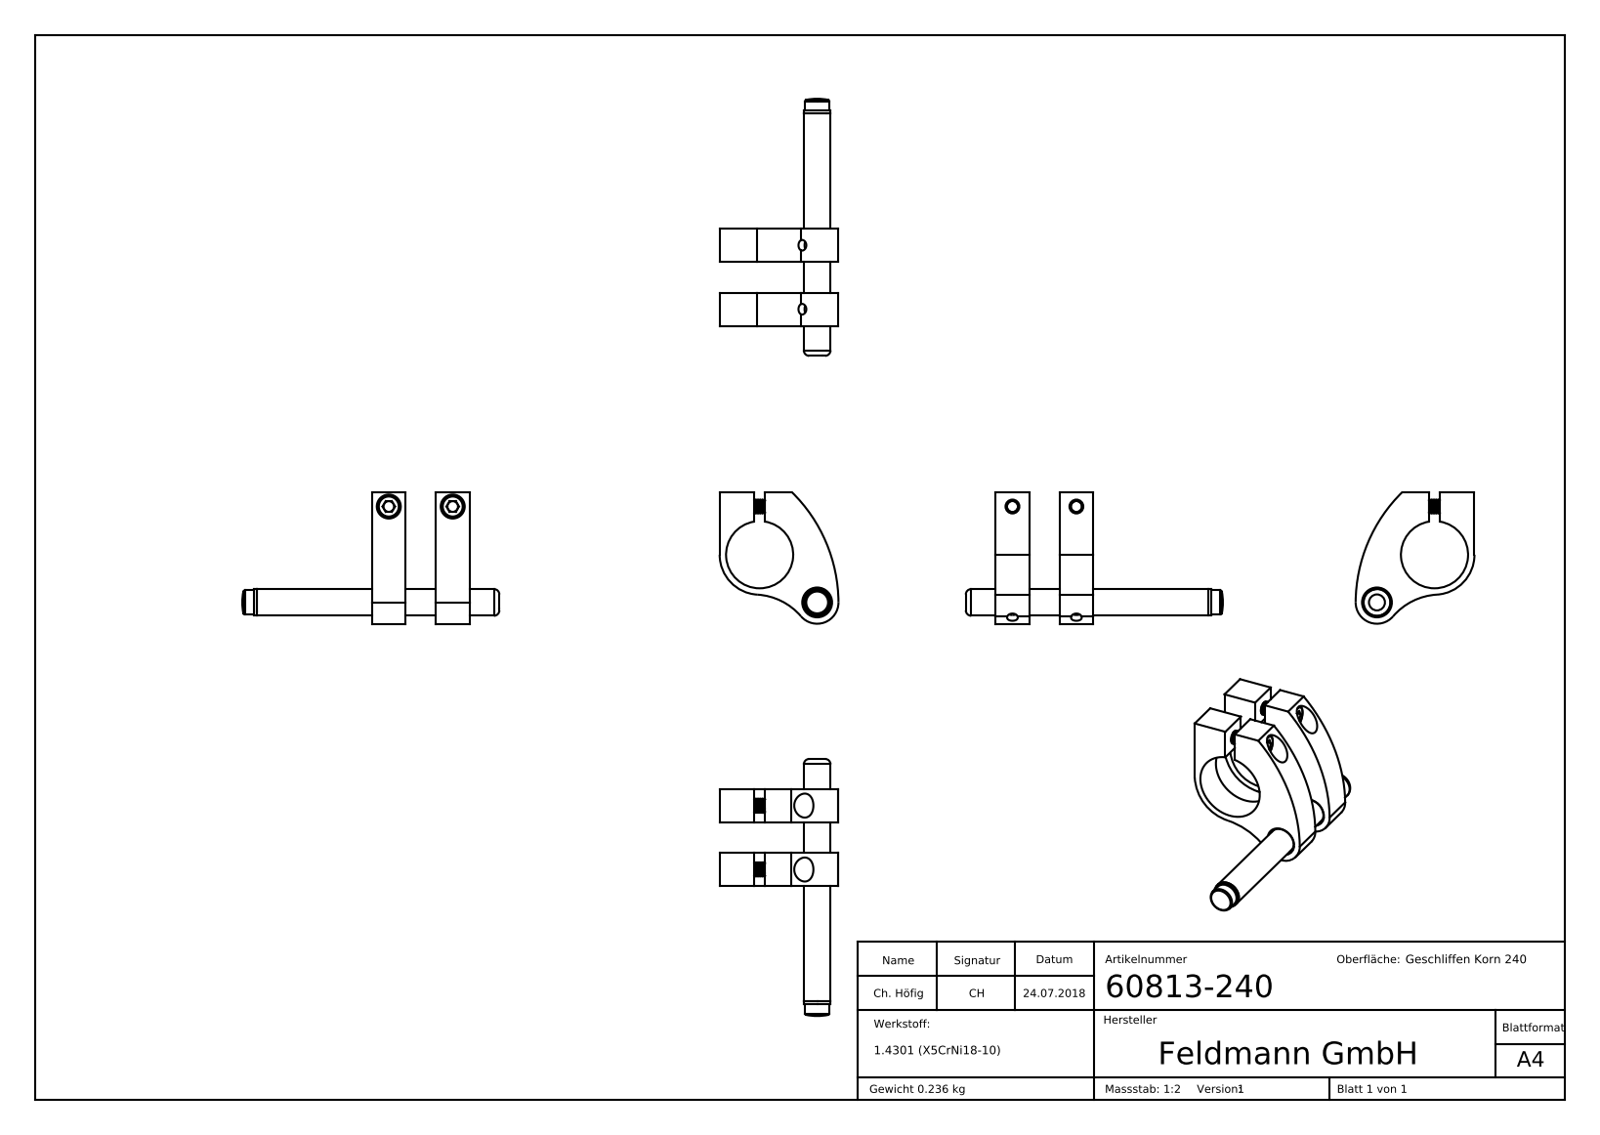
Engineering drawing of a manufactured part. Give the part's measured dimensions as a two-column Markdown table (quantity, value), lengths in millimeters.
| quantity | value |
| --- | --- |
| part name | 60813-240 Teil3_60813-240 Teil3; socket head cap screw_din_DIN 912 M5 x 20 --- 20S; socket set screw cone point_din_DIN 914 - M4 x 6-S; 60813-240 Teil2_60813-240 Teil2 (+2 more) |
| STEP written by | SolidWorks 2015 (CONFIG_CONTROL_DESIGN) |
| units | millimeters |
| bodies | 8 solids, 764 faces (160 planar, 212 cylindrical, 392 other) |
| overall size | 96.5 × 49.5 × 44.6 |
| volume | 31 434 mm³ |
| surface area | 17 352 mm² |
| round holes (diameter × count) | 3.3 × 2, 4 × 2, 4.2 × 2, 5.2 × 2, 5.5 × 2, 9 × 2, 5 × 1, 10.2 × 1, 25.2 × 1 |
| round bosses / shafts (diameter × count) | 8.5 × 2, 5 × 2, 4 × 2, 10 × 1, 9 × 1 |
| partial cylindrical surfaces (radius × count) | 2.6 × 1, 8 × 1, 15 × 1, 23.5 × 1, 58.5 × 1 |
| main face-to-face distances | 24, 12.5, 36.5, 11.5, 13, 17, 4, 22.8, 9.8, 5.8 |
| hole center spacings | 24, 28.05 |
